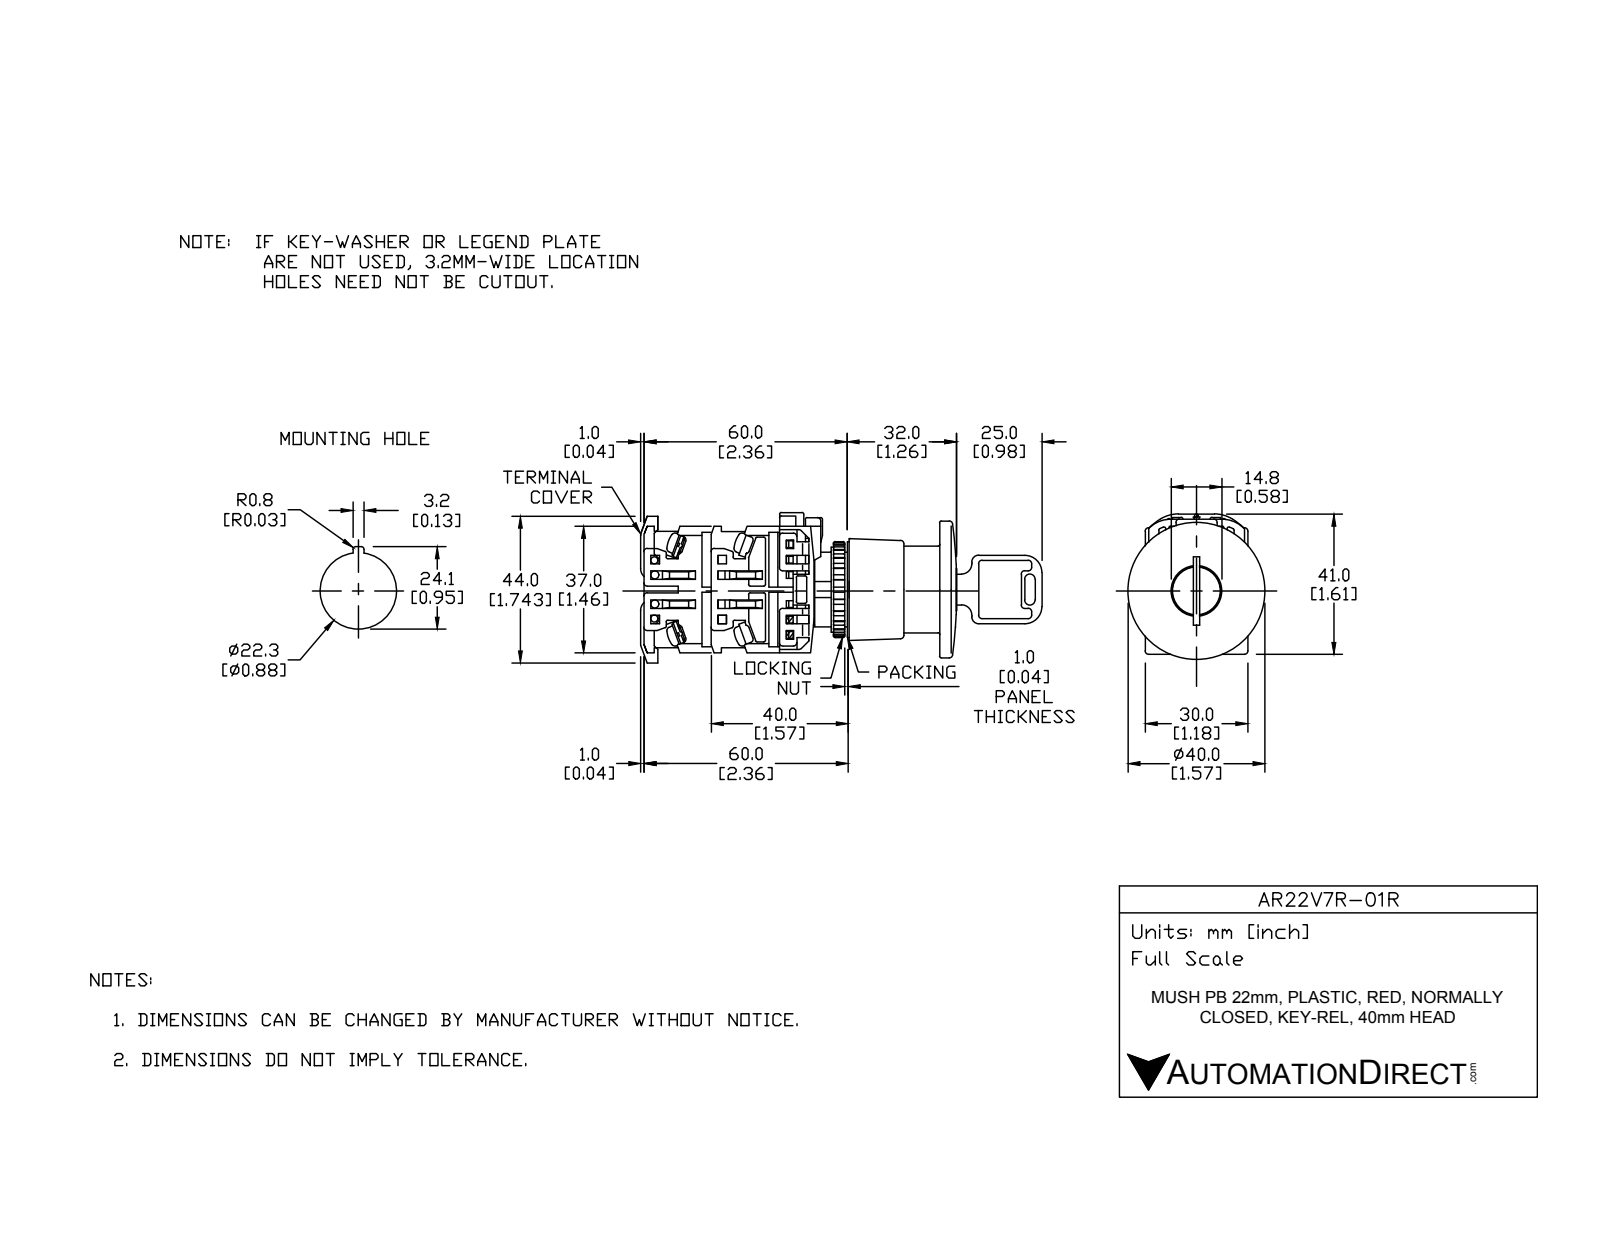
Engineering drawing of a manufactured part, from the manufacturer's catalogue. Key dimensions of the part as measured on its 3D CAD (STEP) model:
Part name (STEP PRODUCT): AR22V7R-01R
STEP written by: SolidWorks 2017 (AUTOMOTIVE_DESIGN)
Units: millimetres
Bodies: 13 solids, 324 faces (226 planar, 76 cylindrical, 22 other)
Overall size (bounding box): 98.5 × 43 × 40
Volume: 37 644 mm³ · Surface area: 23 535 mm²
Round holes (diameter × count): ⌀21.8 ×1, ⌀22 ×1, ⌀25.4 ×1
Round bosses / shafts (diameter × count): ⌀5 ×2, ⌀40 ×1, ⌀29.8 ×1, ⌀25 ×1, ⌀24 ×1, ⌀21.75 ×1, ⌀17 ×1, ⌀14.8 ×1
Partial cylindrical surfaces — rounded edges, fillets, slot ends (radius × count): R0.5 ×23, R1.75 ×4, R2 ×4, R5 ×4, R4 ×2, R16.59 ×1, R17.59 ×1
Main face-to-face distances: 1, 2, 12.5, 10, 18, 22.5, 30, 20.5, 8, 29
